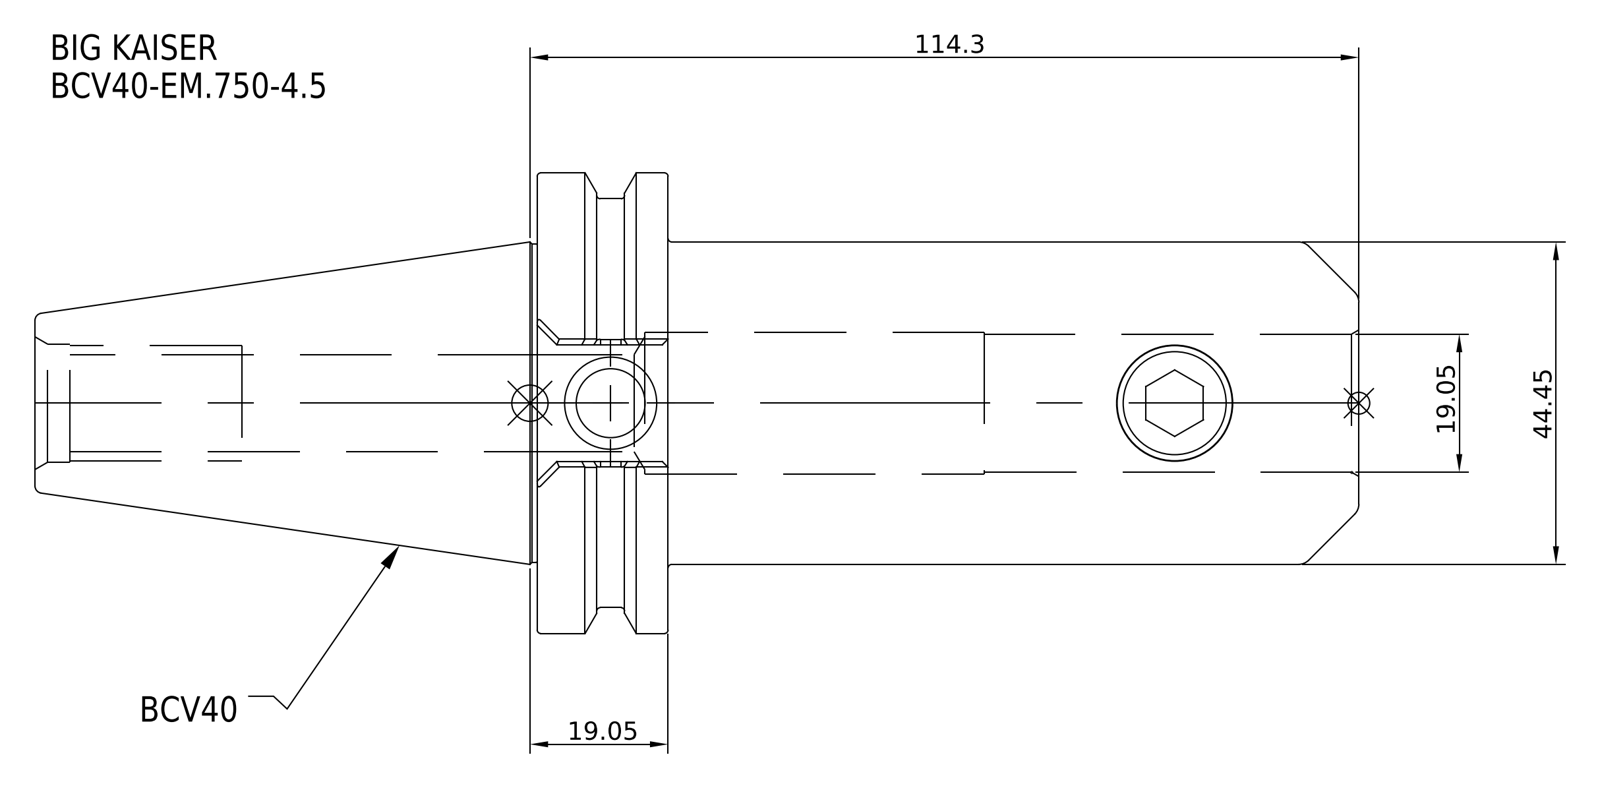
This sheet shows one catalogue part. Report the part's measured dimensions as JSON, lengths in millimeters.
{"part_name": "BCV40-EM_750-4_5", "step_written_by": "SolidWorks 2021 (CONFIG_CONTROL_DESIGN)", "units": "millimeters", "bodies": {"solids": 1, "faces": 27, "planar": 7, "cylindrical": 12, "other": 8}, "overall_size": [182.55, 63.5, 63.5], "volume_mm3": 242563, "surface_area_mm2": 34611, "round_holes": [[19.05, 1]], "round_bosses_or_shafts": [[63.5, 1], [56.36, 1], [44.45, 1]], "face_to_face_distances": [18.05, 87.3, 69.25, 95.25, 113.3, 182.55, 79.25, 16, 34.05, 103.3]}
